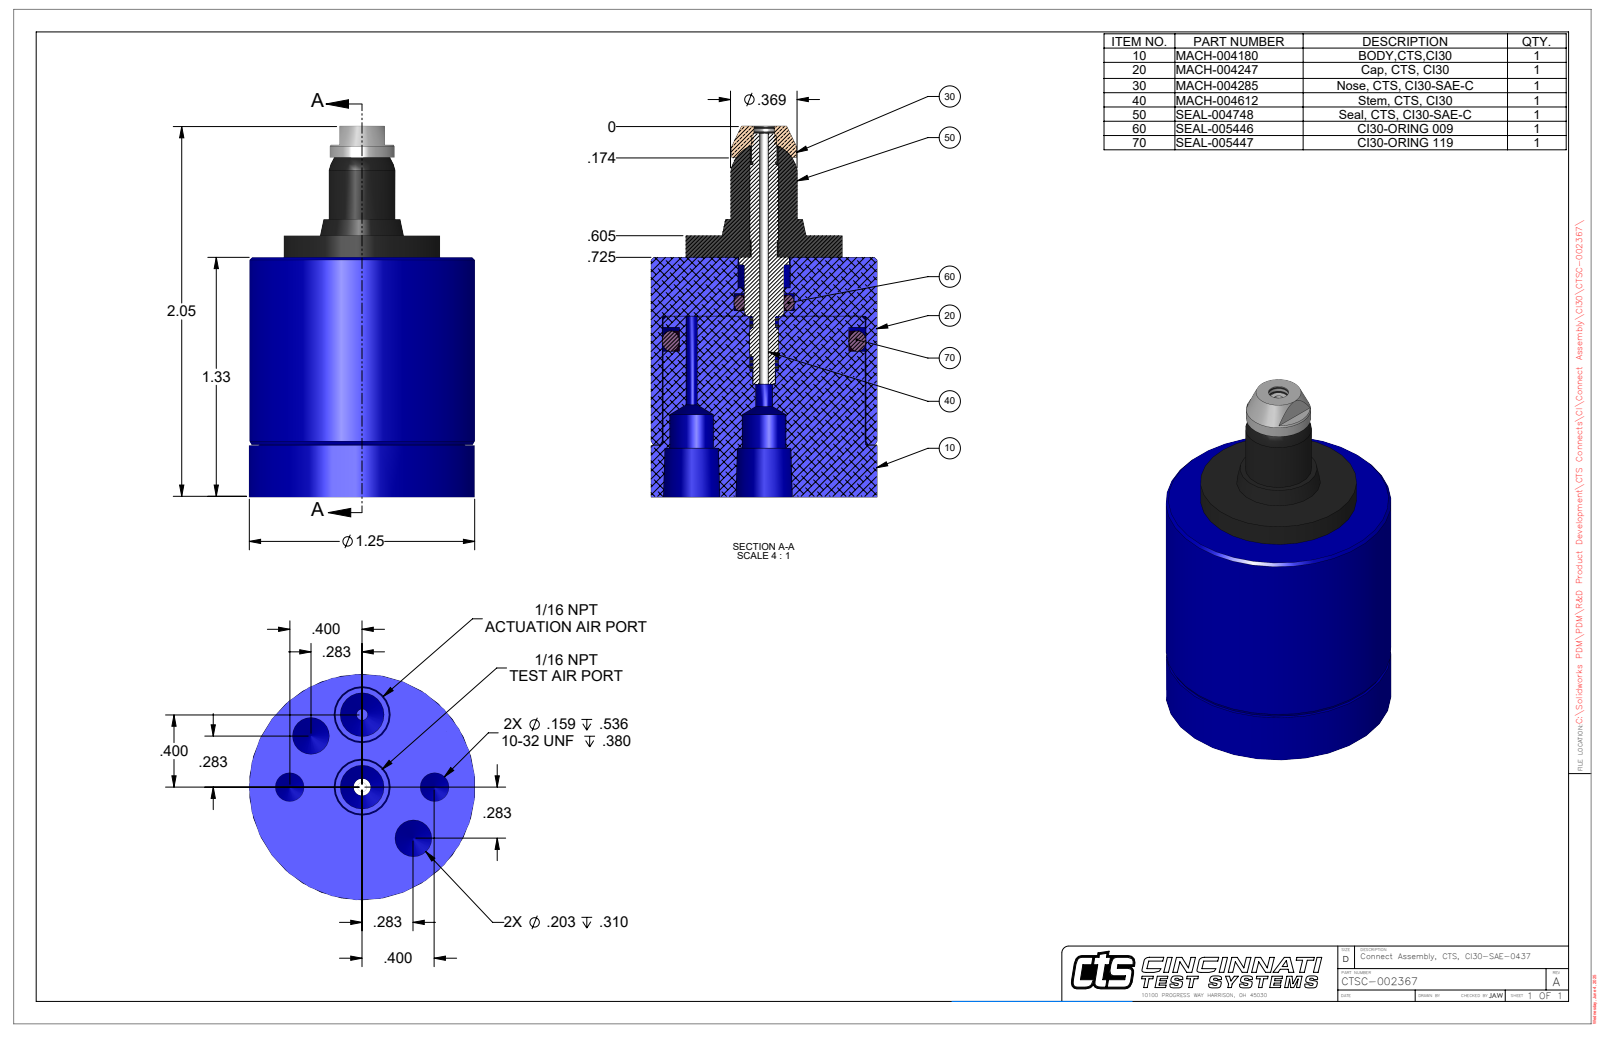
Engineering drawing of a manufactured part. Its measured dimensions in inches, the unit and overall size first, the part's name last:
Units: inches
Overall size (bounding box): 2.05 × 1.25 × 1.25
Round holes (diameter × count): ⌀0.159 ×2, ⌀0.203 ×2, ⌀0.242 ×2, ⌀0.052 ×1, ⌀0.062 ×1, ⌀0.094 ×1, ⌀0.113 ×1, ⌀0.289 ×1, ⌀1.125 ×1
Round bosses / shafts (diameter × count): ⌀1.25 ×1, ⌀1.115 ×1, ⌀0.865 ×1, ⌀0.369 ×1, ⌀0.36 ×1, ⌀0.277 ×1
Main face-to-face distances: 1.325, 1.445, 0.12, 0.287, 1.039, 1.158, 0.29, 1.035, 1.155, 0.271
Hole centre spacings: 0.306, 0.4, 0.739, 0.4, 0.566, 0.8, 0.8
Volume: 1.646 in³ · Surface area: 13.5 in²
Bodies: 2 solids, 90 faces (19 planar, 38 cylindrical, 33 other)
Part name (STEP PRODUCT): CTSC-002367
STEP written by: SolidWorks 2023 (AUTOMOTIVE_DESIGN)
